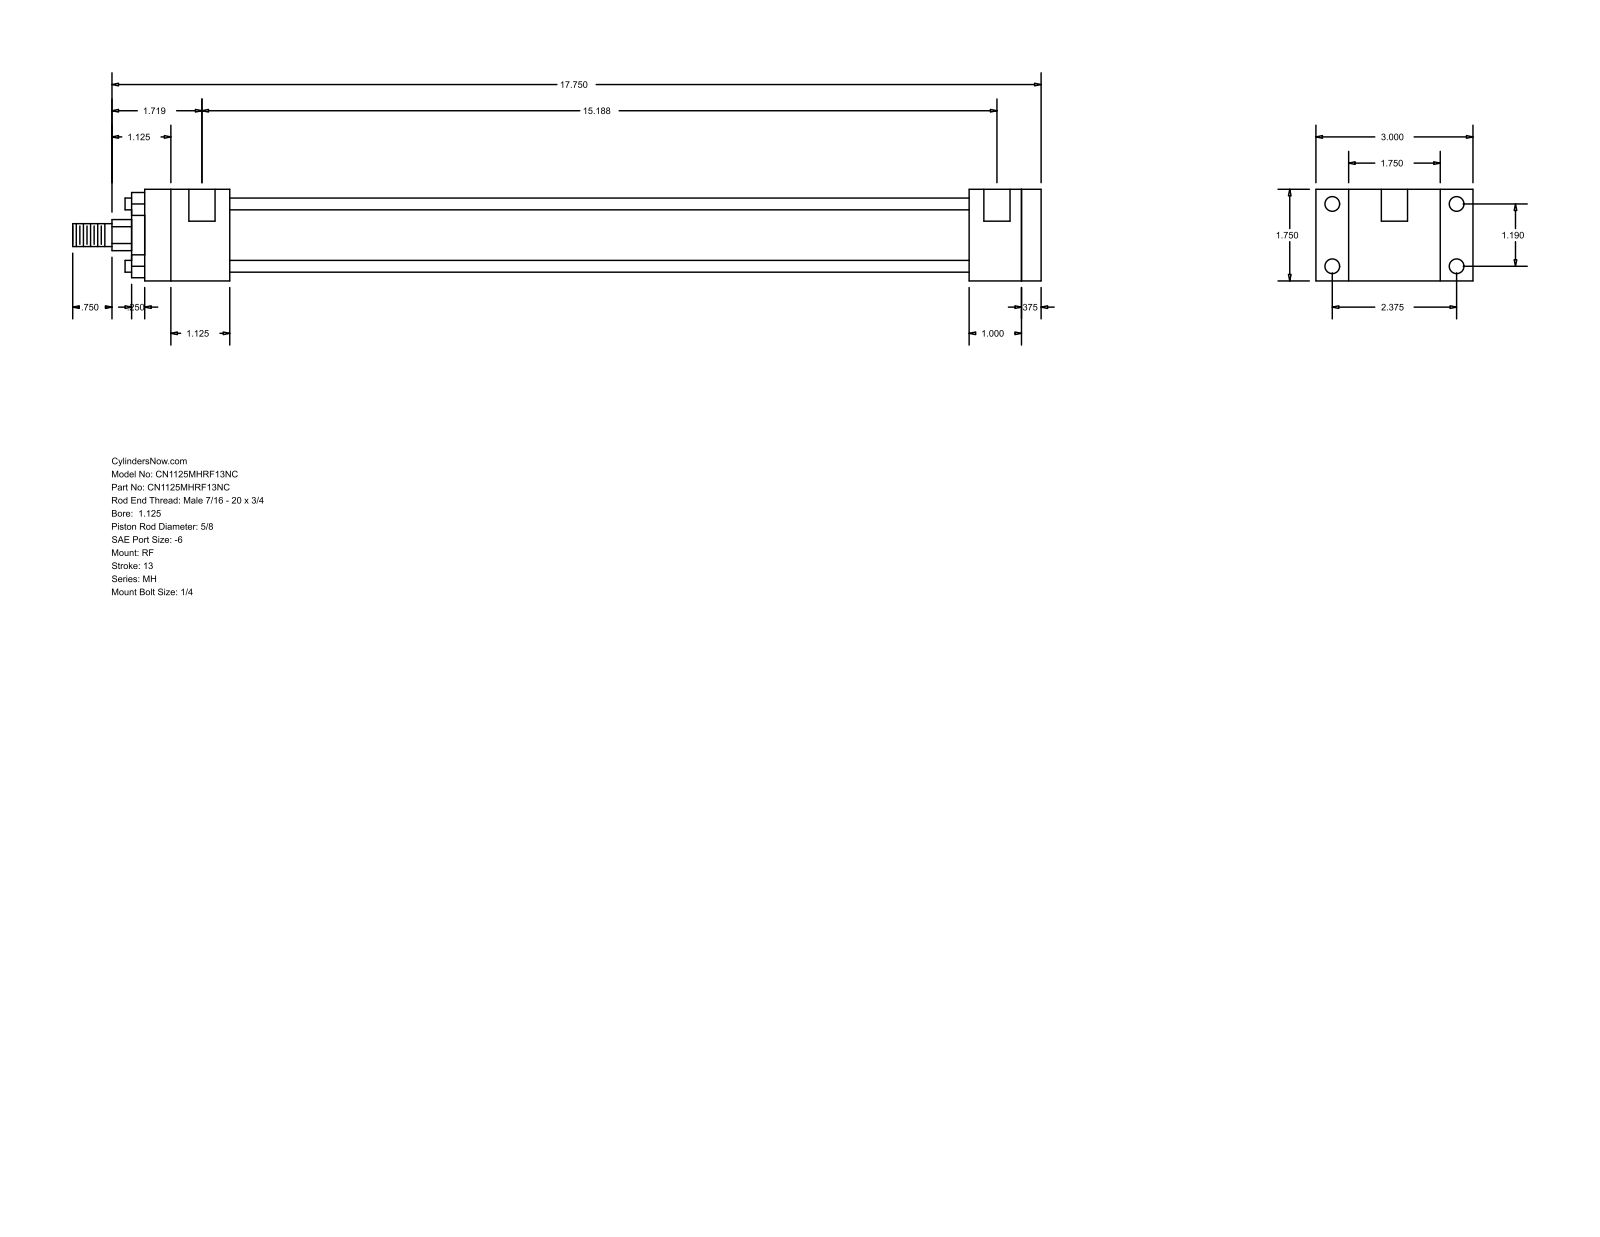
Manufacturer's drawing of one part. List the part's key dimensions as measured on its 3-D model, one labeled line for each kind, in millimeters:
Part name (STEP PRODUCT): MH_RF__0112_0.625
STEP written by: GSSL Pune (CONFIG_CONTROL_DESIGN)
Units: millimetres
Bodies: 0 solids, 92 faces (64 planar, 28 cylindrical, 0 other)
Overall size (bounding box): 469.9 × 76.2 × 44.45
Round holes (diameter × count): ⌀5.56 ×4, ⌀7.14 ×4, ⌀12.7 ×2
Round bosses / shafts (diameter × count): ⌀5.71 ×4, ⌀34.92 ×1, ⌀28.57 ×1, ⌀15.88 ×1, ⌀11.11 ×1
Partial cylindrical surfaces — rounded edges, fillets, slot ends (radius × count): R7.54 ×1
Main face-to-face distances: 44.46, 9.53, 434.97, 15.87, 384.17, 393.7, 358.78, 25.39, 34.92, 41.27
Hole centre spacings: 30.22, 60.32, 67.47, 382.59, 3.17, 385.76
